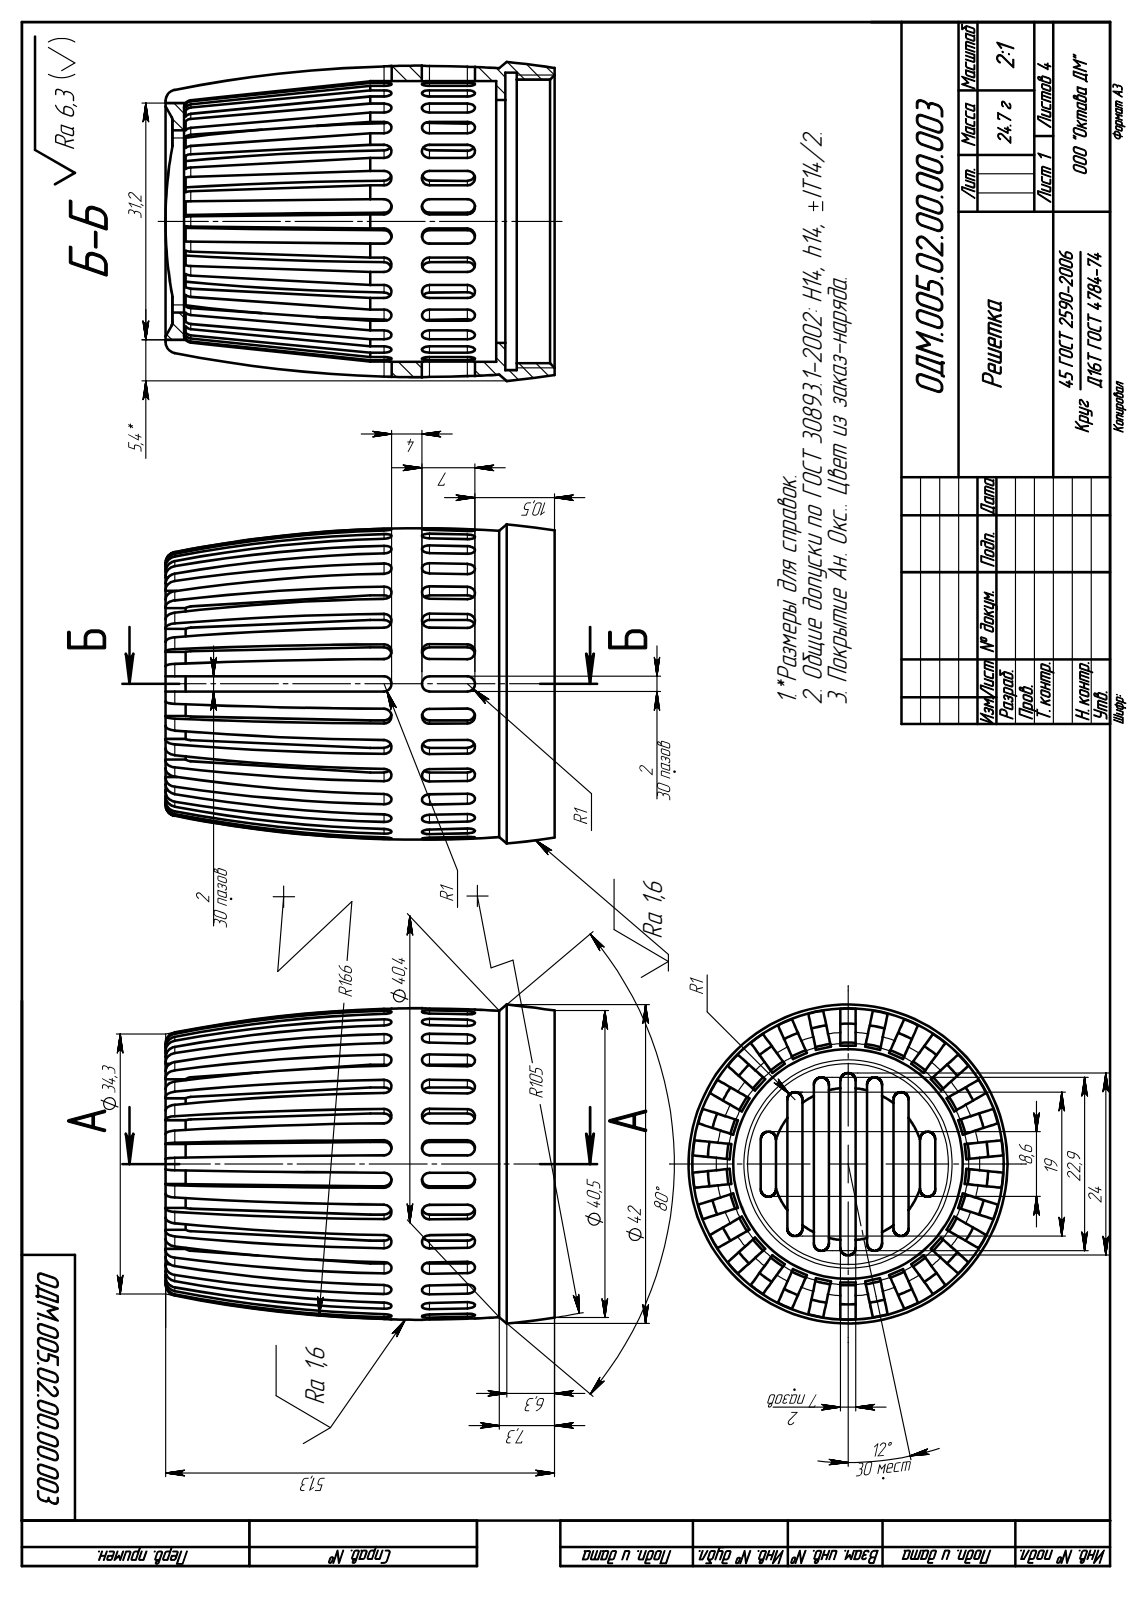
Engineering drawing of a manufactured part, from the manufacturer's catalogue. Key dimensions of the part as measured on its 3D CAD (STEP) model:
Part name (STEP PRODUCT): ОДМ.005.02.00.00.003 Решетка
STEP written by: SolidWorks 2017 (AUTOMOTIVE_DESIGN)
Units: millimetres
Bodies: 1 solid, 376 faces (171 planar, 119 cylindrical, 86 other)
Overall size (bounding box): 51.3 × 42.05 × 42.05
Volume: 8 873 mm³ · Surface area: 15 128 mm²
Round holes (diameter × count): ⌀32 ×1, ⌀37 ×1, ⌀37.4 ×1, ⌀39.2 ×1
Partial cylindrical surfaces — rounded edges, fillets, slot ends (radius × count): R1 ×81
Main face-to-face distances: 2, 1.5, 42.36, 3.5, 43.86, 41.16, 1.2, 7, 5, 42.66
